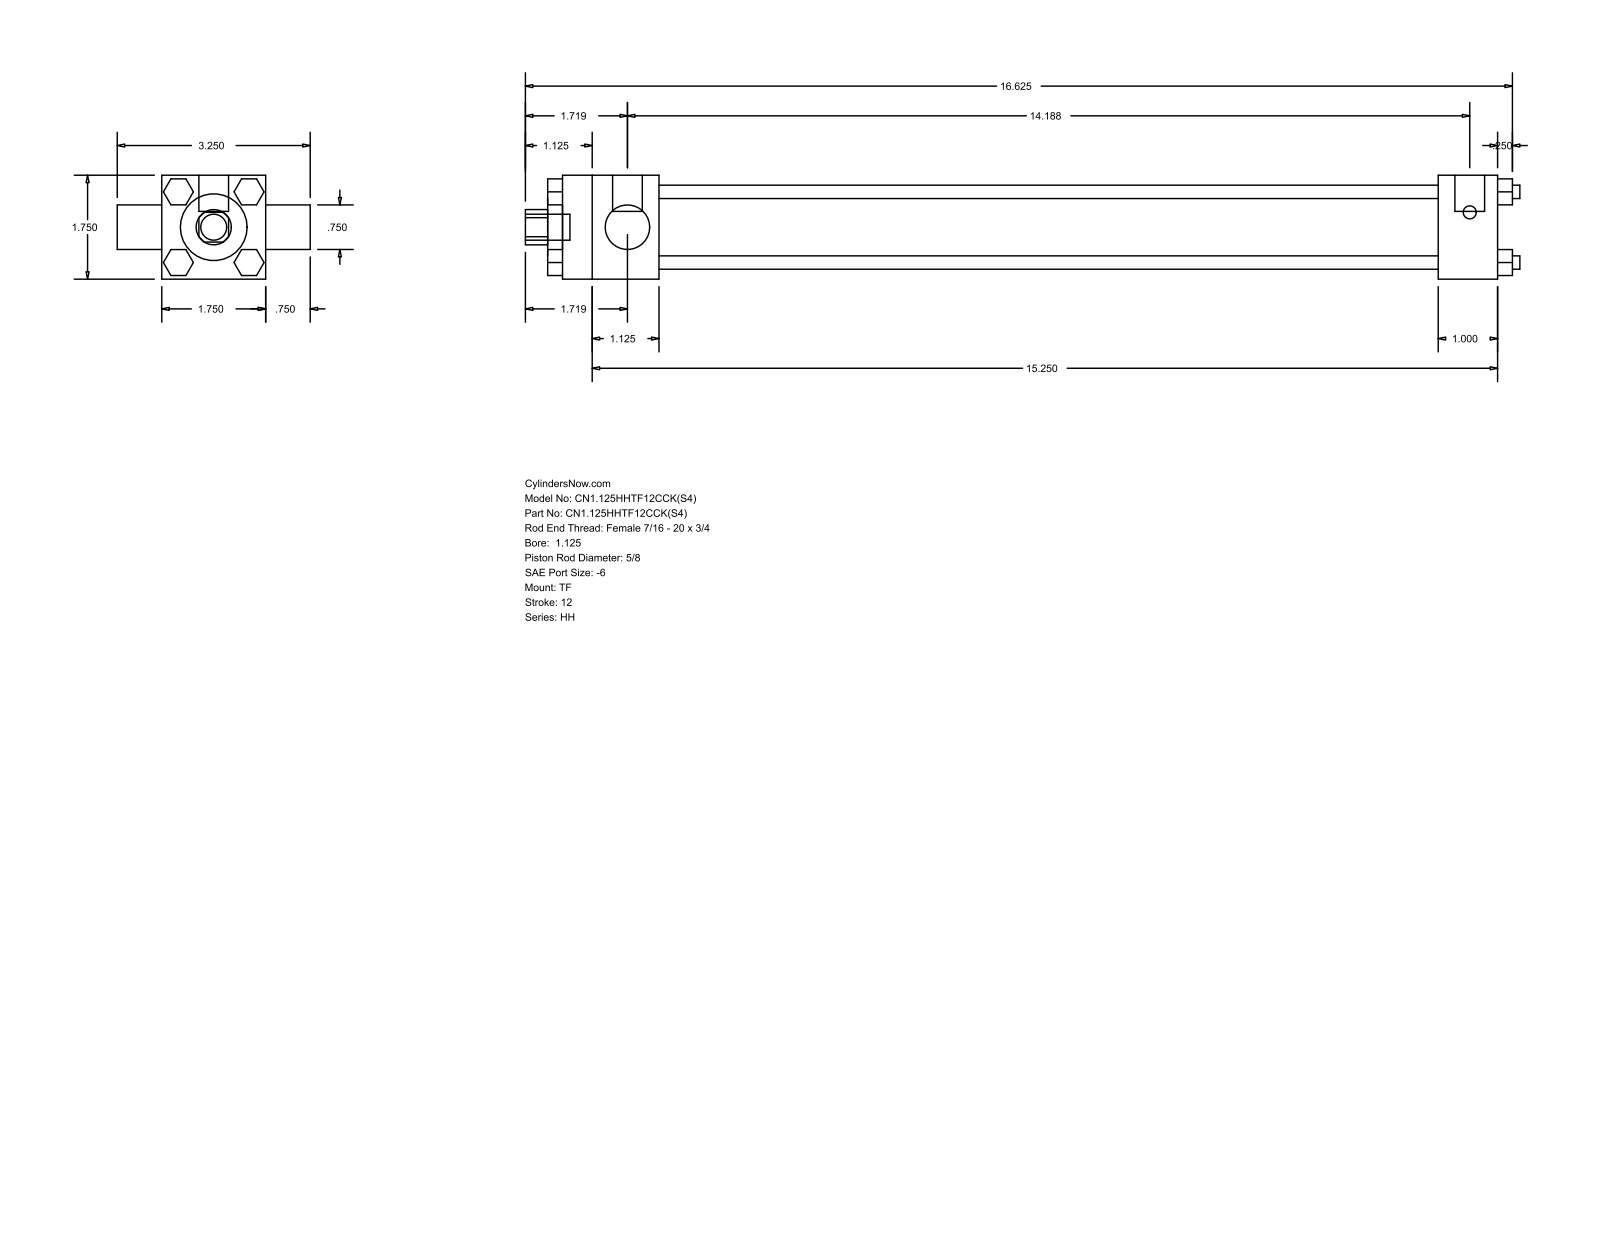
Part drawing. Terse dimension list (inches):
name: HH_TF__0112_0.625
written by: GSSL Pune (CONFIG_CONTROL_DESIGN)
unit: in
bodies: 0 solids, 120 faces (92 planar, 28 cylindrical, 0 other)
size: 16.75 × 3.25 × 1.75
holes: 1× ⌀0.625, 1× ⌀0.75, 1× ⌀1.125, 1× ⌀1.375
bosses: 4× ⌀0.225, 3× ⌀0.219, 2× ⌀0.5, 1× ⌀0.437
rounds: 1× R0.297
face distances: 1.75, 0.437, 13.125, 14.125, 1, 1.625, 14.75, 15.75, 1.875, 16
